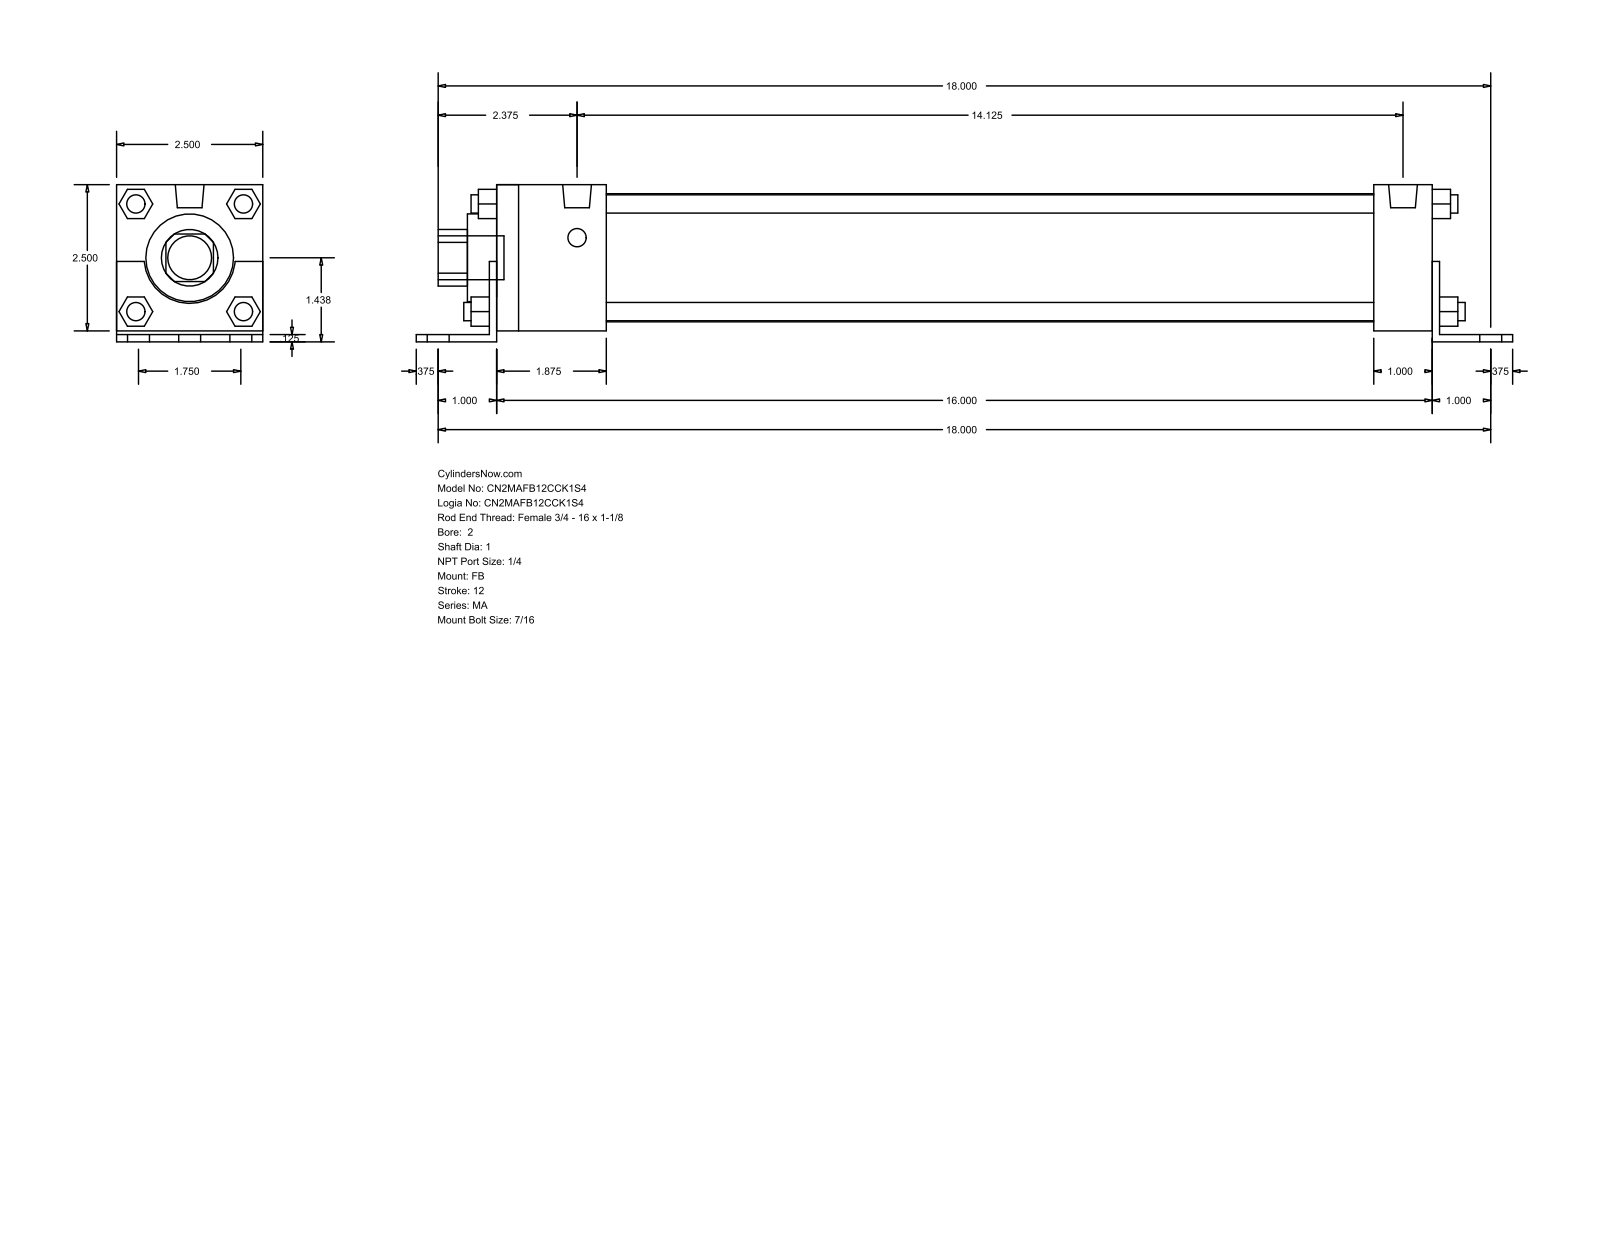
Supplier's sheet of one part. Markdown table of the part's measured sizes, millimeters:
| quantity | value |
| --- | --- |
| part name | MA_FB__0200_1 |
| STEP written by | GSSL Pune (CONFIG_CONTROL_DESIGN) |
| units | millimeters |
| bodies | 0 solids, 140 faces (105 planar, 35 cylindrical, 0 other) |
| overall size | 476.25 × 68.26 × 63.5 |
| round holes (diameter × count) | 25.4 × 1, 38.1 × 1, 55.63 × 1 |
| round bosses / shafts (diameter × count) | 7.94 × 8, 11.11 × 6, 12.49 × 2, 19.05 × 1 |
| partial cylindrical surfaces (radius × count) | 12.29 × 1, 19.81 × 1 |
| main face-to-face distances | 63.5, 3.17, 4.76, 68.26, 1.59, 65.09, 12.7, 3.18, 406.4, 409.58 |
